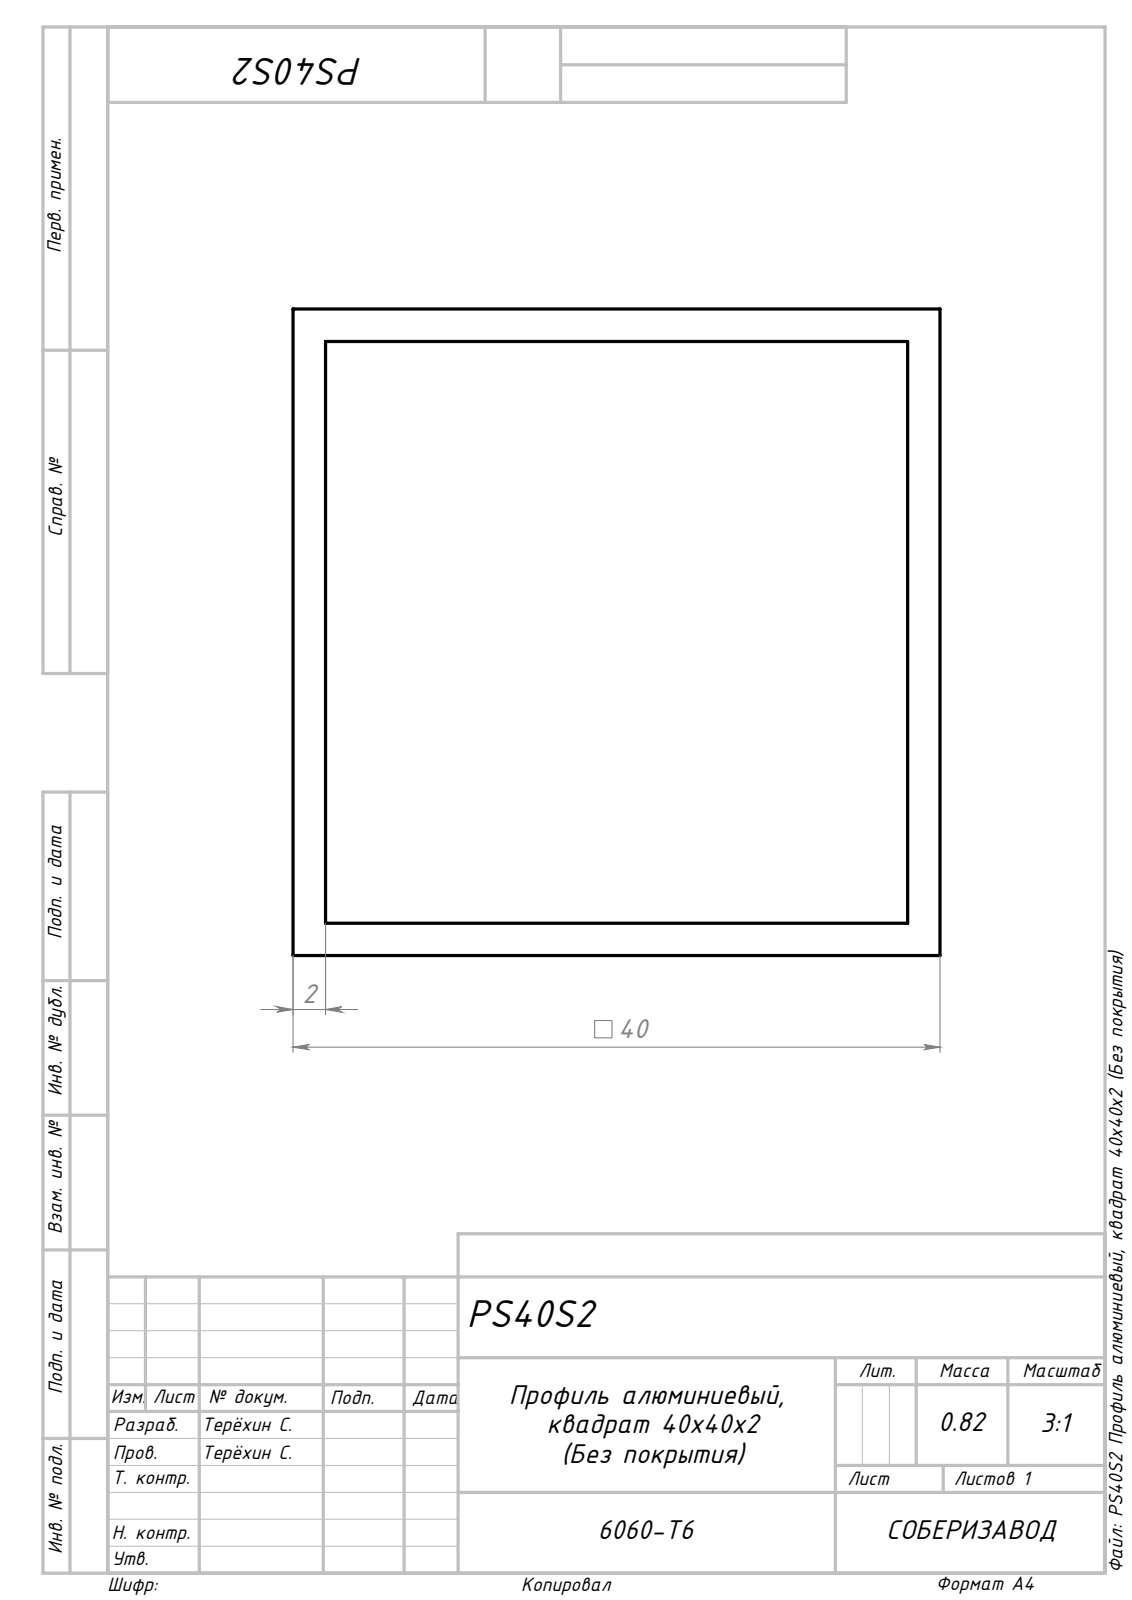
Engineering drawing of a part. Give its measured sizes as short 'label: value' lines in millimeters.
name: Сборка2; PS40S2 Профиль алюминиевый, квадрат 40x40x2 (Без покрытия)_00
written by: SolidWorks 2024 (AUTOMOTIVE_DESIGN)
unit: mm
bodies: 1 solid, 10 faces (10 planar, 0 cylindrical, 0 other)
size: 1000 × 40 × 40
volume: 304 000 mm³; area: 304 608 mm²
face distances: 2, 38, 40, 36, 1000
